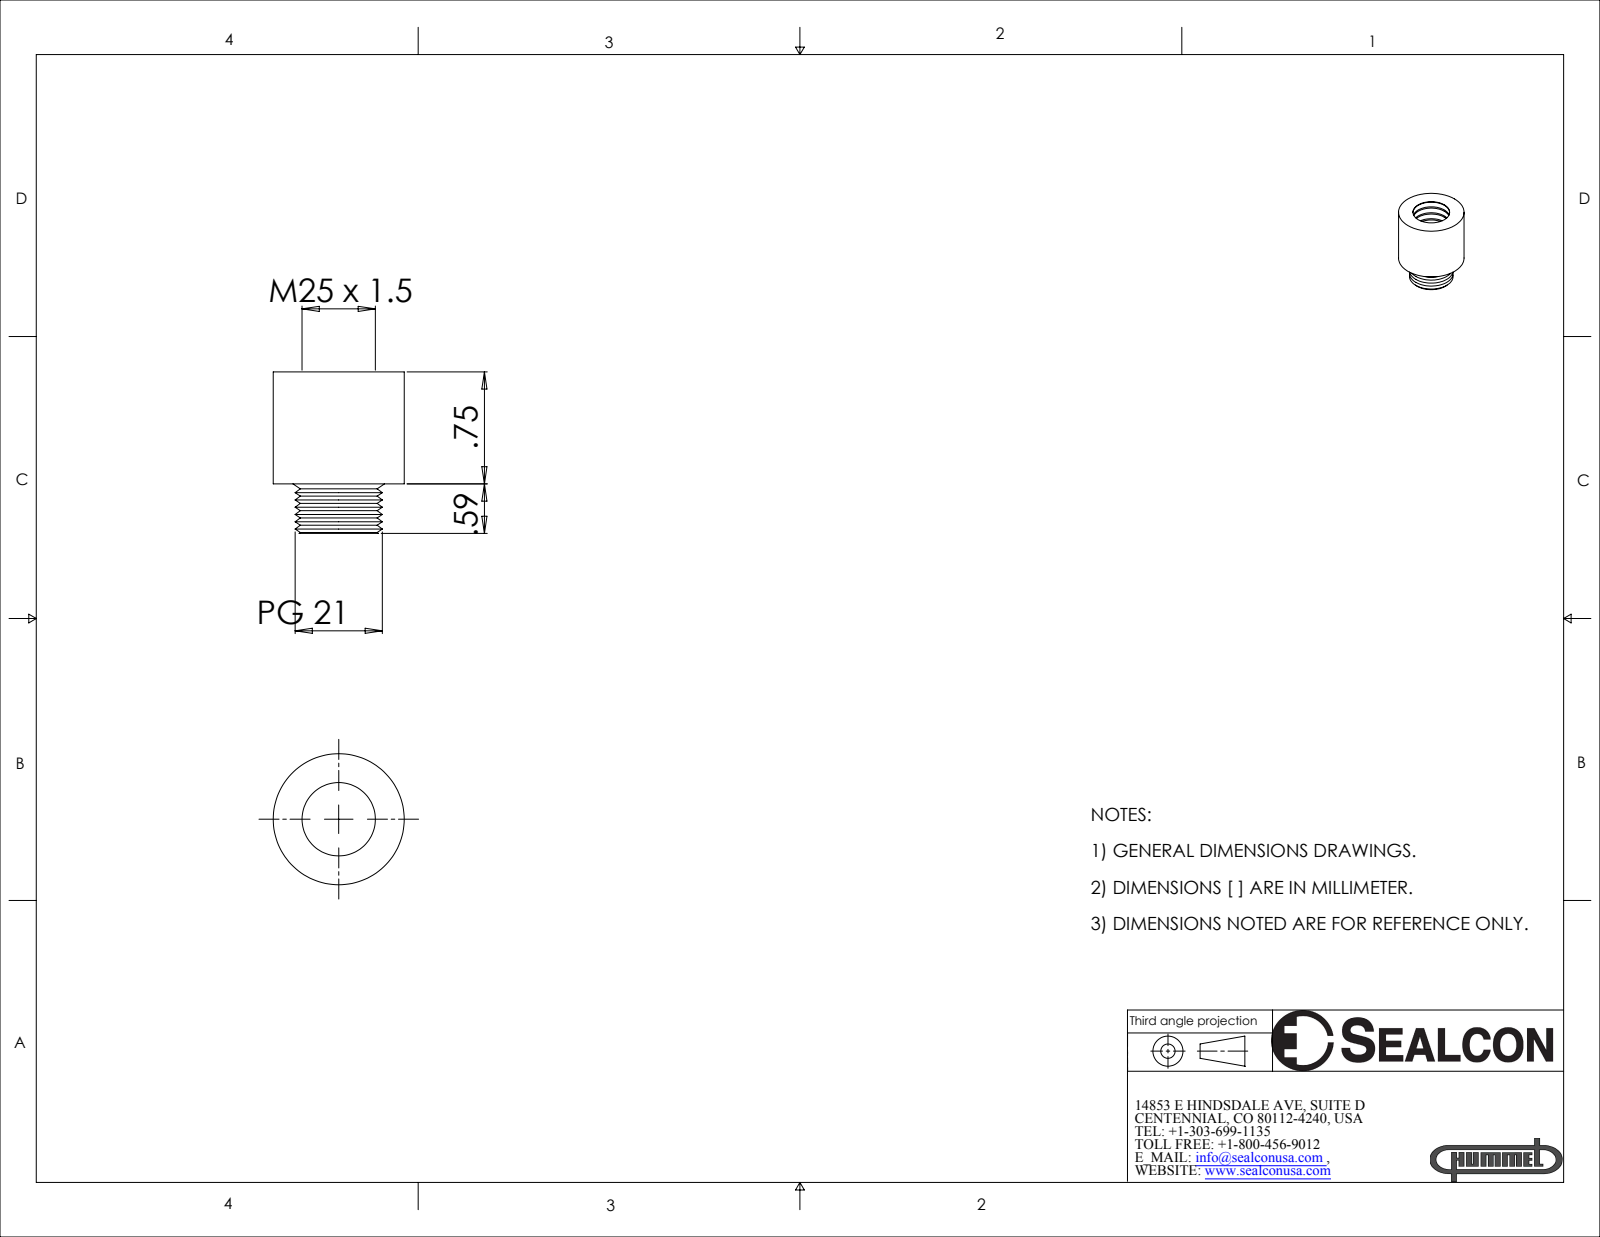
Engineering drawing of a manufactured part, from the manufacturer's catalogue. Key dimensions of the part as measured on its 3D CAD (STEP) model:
Part name (STEP PRODUCT): AP-2125-BK
STEP written by: SolidWorks 2008 (CONFIG_CONTROL_DESIGN)
Units: inches
Bodies: 1 solid, 77 faces (3 planar, 18 cylindrical, 56 other)
Overall size (bounding box): 1.11 × 0.901 × 0.901
Volume: 0.328 in³ · Surface area: 6.601 in²
Round holes (diameter × count): ⌀0.504 ×1
Round bosses / shafts (diameter × count): ⌀0.901 ×1
Main face-to-face distances: 0.77, 0.34, 1.11
